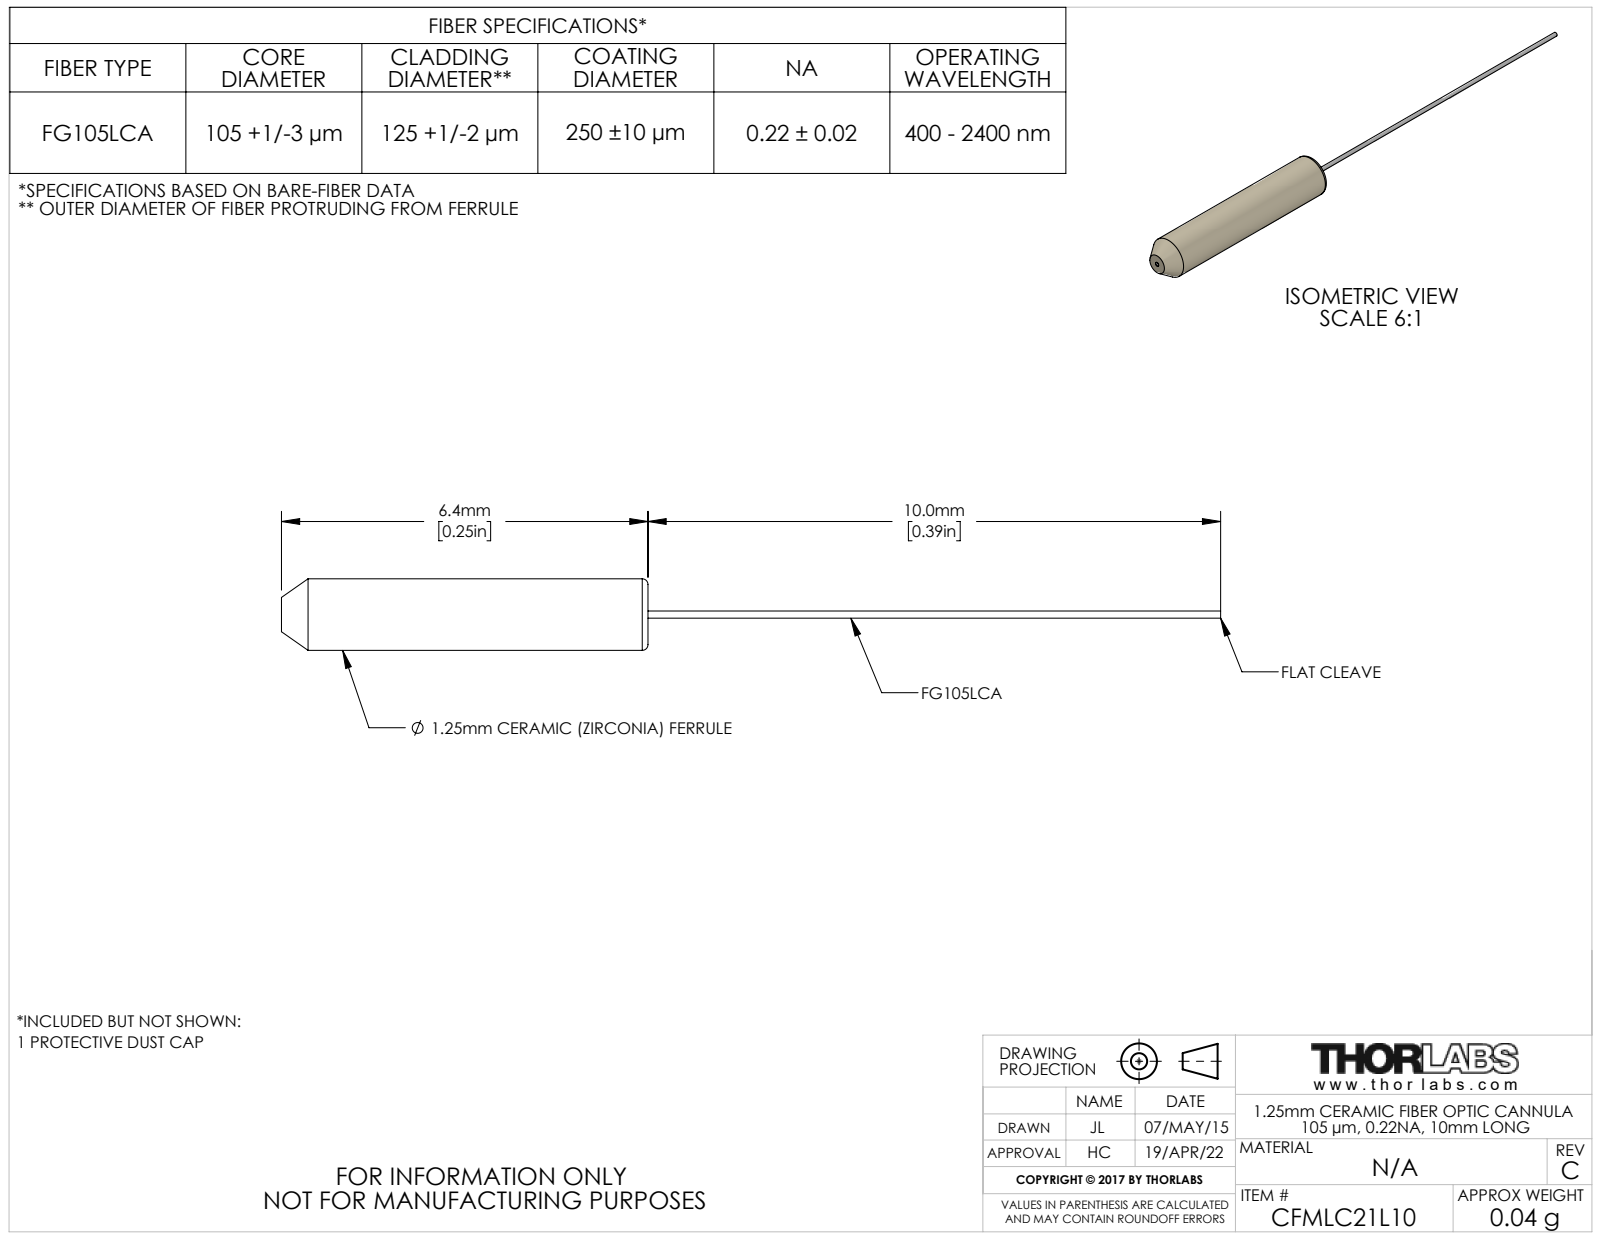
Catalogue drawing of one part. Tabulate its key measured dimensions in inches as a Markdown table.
| quantity | value |
| --- | --- |
| part name | TTN041721-E0W |
| STEP written by | SolidWorks 2014 (CONFIG_CONTROL_DESIGN) |
| units | inches |
| bodies | 2 solids, 18 faces (4 planar, 6 cylindrical, 8 other) |
| overall size | 0.646 × 0.049 × 0.049 |
| round bosses / shafts (diameter × count) | 0.049 × 1 |
| main face-to-face distances | 0.252, 0.646, 0.394 |
